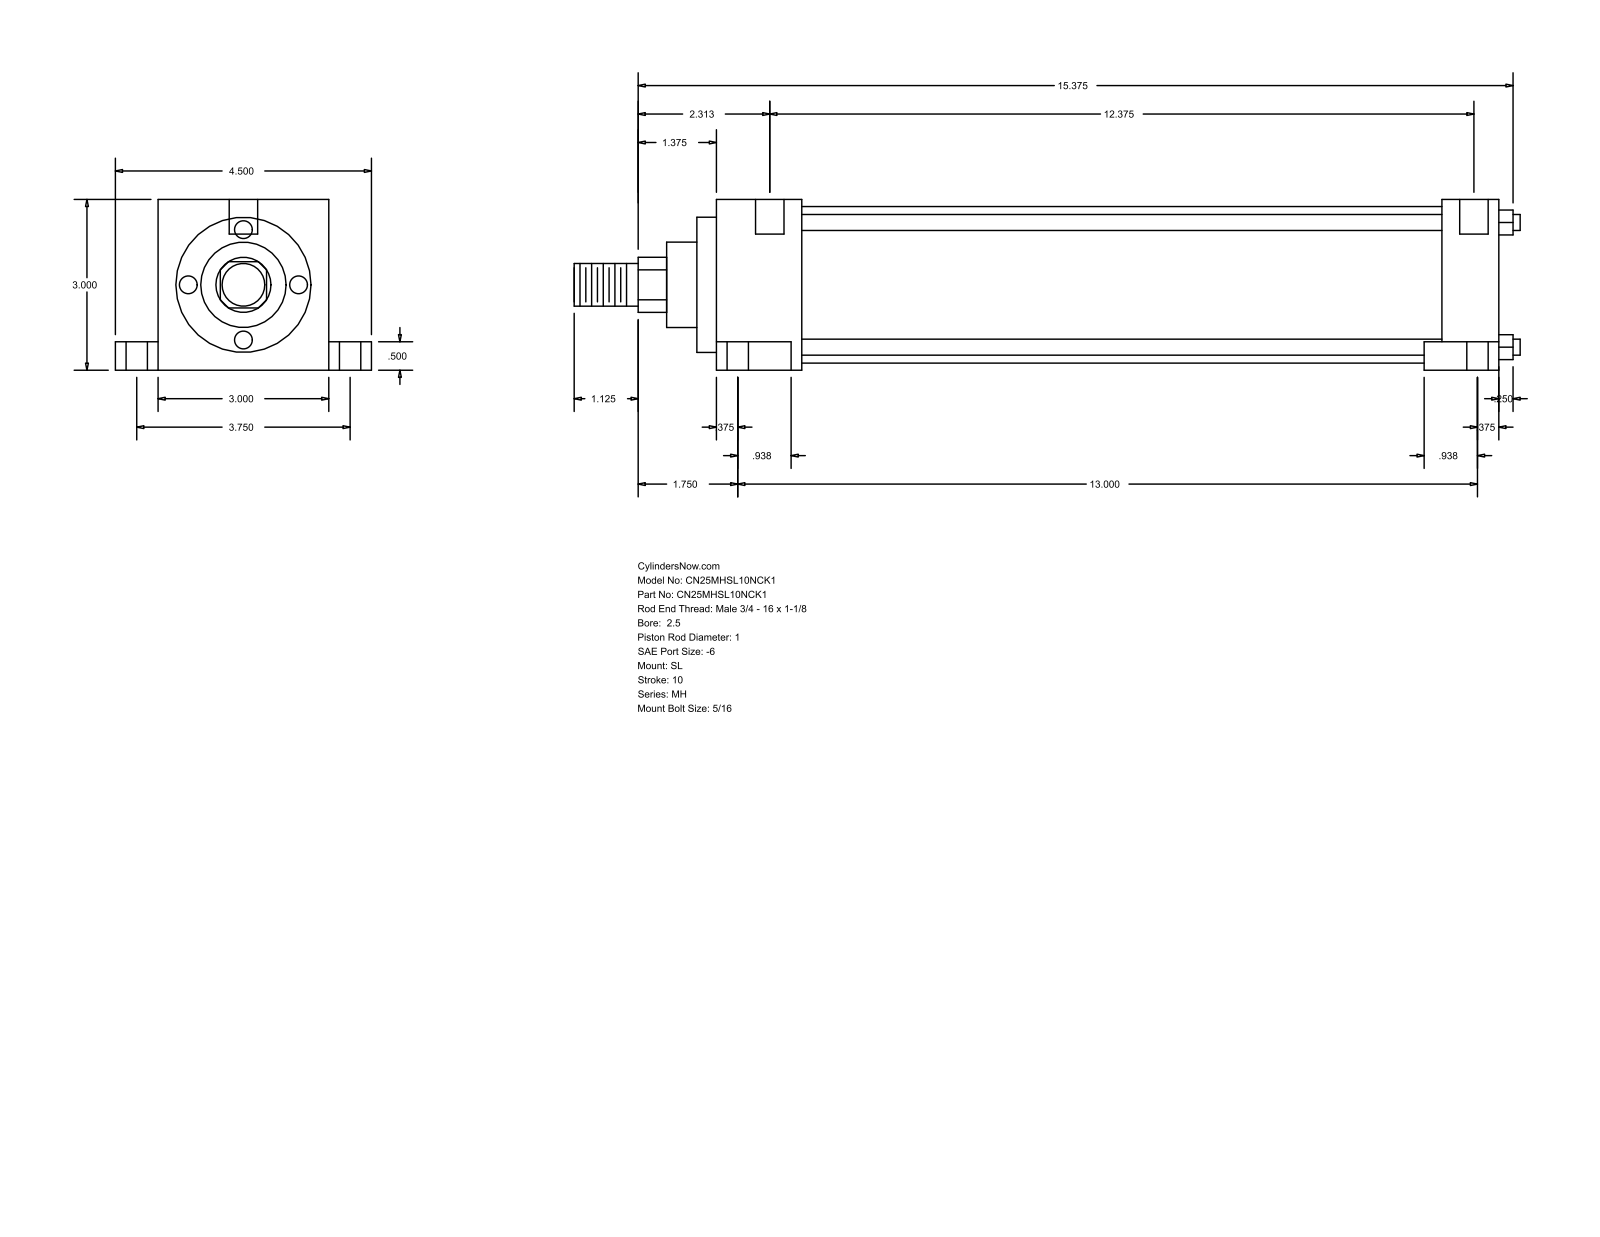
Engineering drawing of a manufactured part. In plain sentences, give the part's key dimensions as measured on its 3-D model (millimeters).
The part is named "MH_SL__0250_1". Its 3-D file was written by "GSSL Pune (CONFIG_CONTROL_DESIGN)". It is 0 solids with 86 faces: 61 planar, 25 cylindrical and 0 other. Overall it measures 422.27 by 114.3 by 76.2 millimeters. Round holes: 2 of diameter 5.56, 2 of diameter 9.53, 2 of diameter 15.88, 1 of diameter 12.7. Round bosses or shafts: 4 of diameter 7.14, 1 of diameter 69.85, 1 of diameter 60.33, 1 of diameter 38.1, 1 of diameter 25.4, 1 of diameter 19.05. Partial cylindrical surfaces (rounded edges, fillets, slot ends): 1 of radius 12.29. The main face-to-face distances are 76.2, 25.41, 332.58, 357.99, 12.7, 63.5, 19.05, 95.25, 13.49, 346.07. The hole center spacings are 47.65, 3.18, 95.24.
